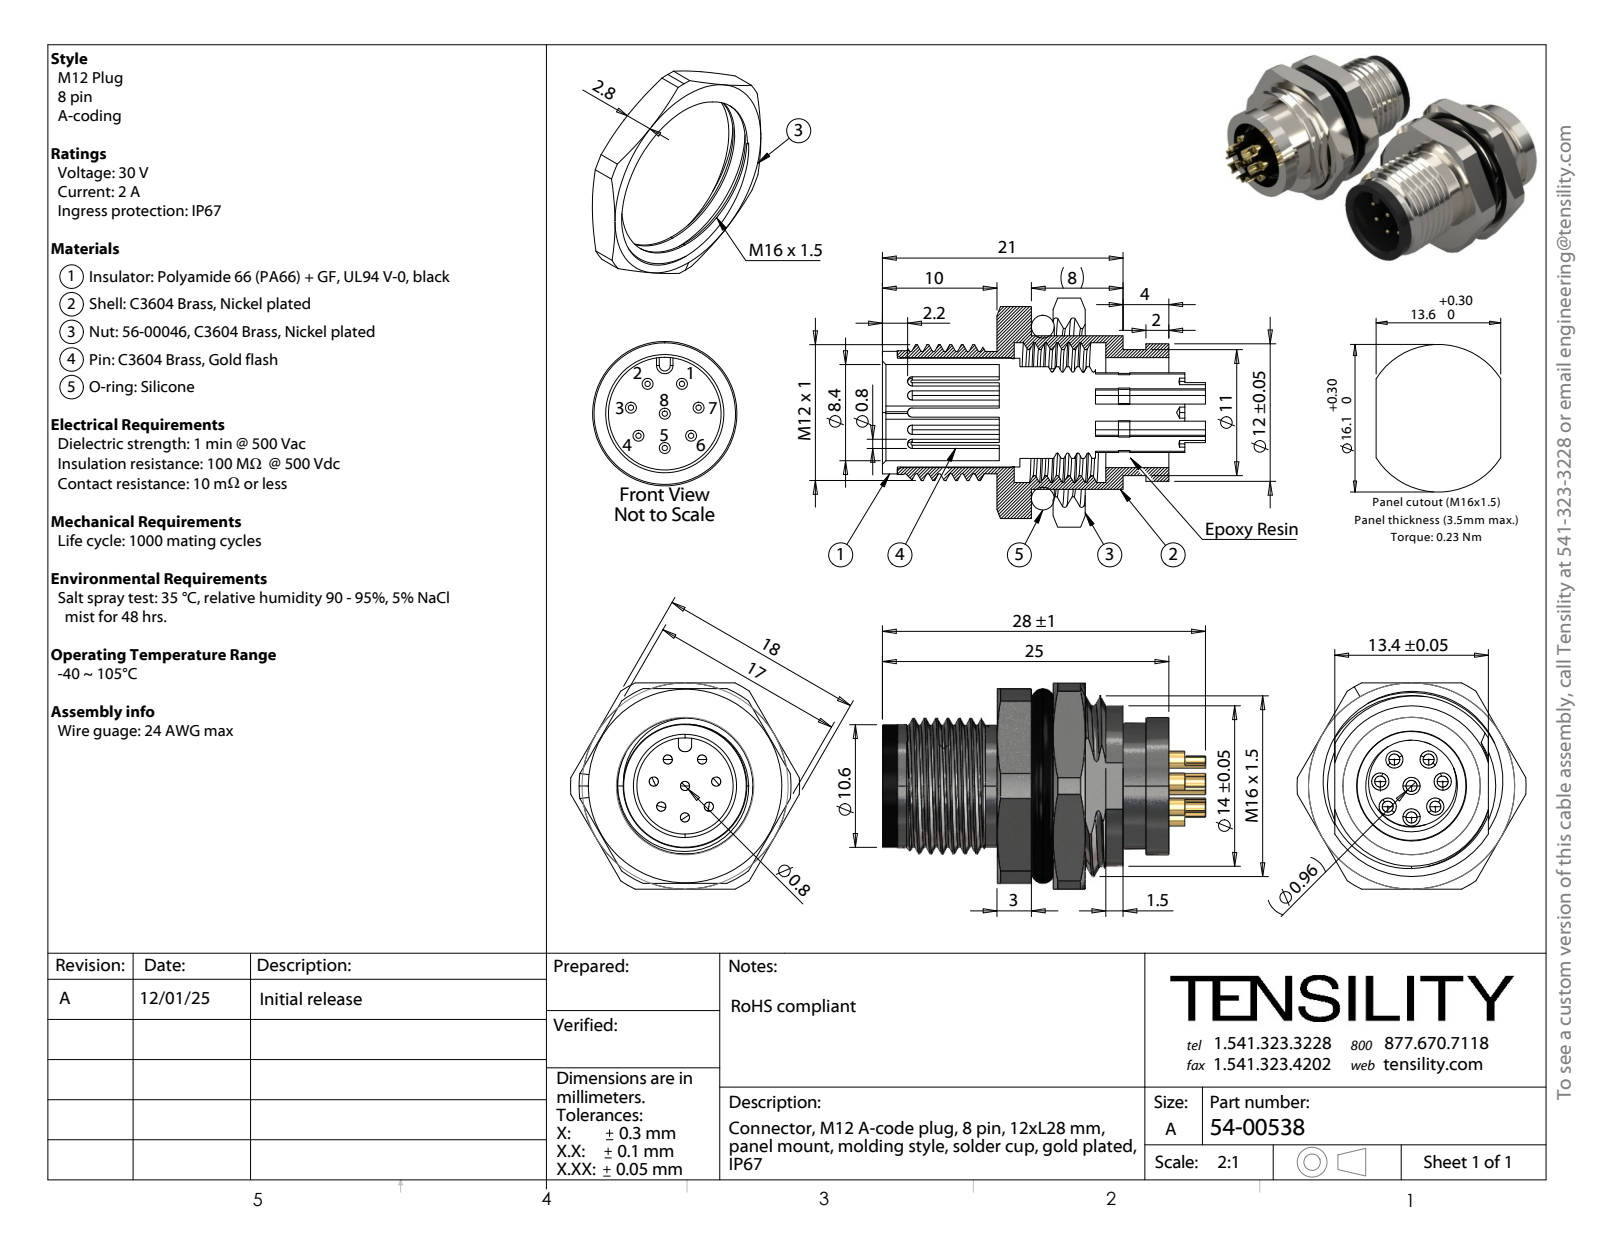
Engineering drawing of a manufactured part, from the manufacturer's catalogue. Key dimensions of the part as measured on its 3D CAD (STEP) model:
Part name (STEP PRODUCT): 54-00538; 56-00046
STEP written by: SolidWorks 2025 (CONFIG_CONTROL_DESIGN)
Units: millimetres
Bodies: 4 solids, 389 faces (81 planar, 182 cylindrical, 126 other)
Overall size (bounding box): 28.2 × 20 × 18
Volume: 2 456 mm³ · Surface area: 5 061 mm²
Round holes (diameter × count): ⌀0.96 ×8, ⌀8.4 ×1, ⌀9.4 ×1, ⌀9.6 ×1, ⌀12.2 ×1, ⌀14.7 ×1
Round bosses / shafts (diameter × count): ⌀1.5 ×8, ⌀1.4 ×8, ⌀0.8 ×8, ⌀14 ×1, ⌀13.94 ×1, ⌀12 ×1, ⌀11.86 ×1, ⌀11 ×1
Partial cylindrical surfaces — rounded edges, fillets, slot ends (radius × count): R0.5 ×2, R2.75 ×1, R7.9 ×1, R9.25 ×1, R10 ×1
Main face-to-face distances: 1.5, 0.5, 4.7, 2.8, 8, 3, 9.5, 11, 1.3, 7.5
Hole centre spacings: 2.28, 4.15, 2.75, 2.76, 4.64, 5.27, 5.28, 5.44
